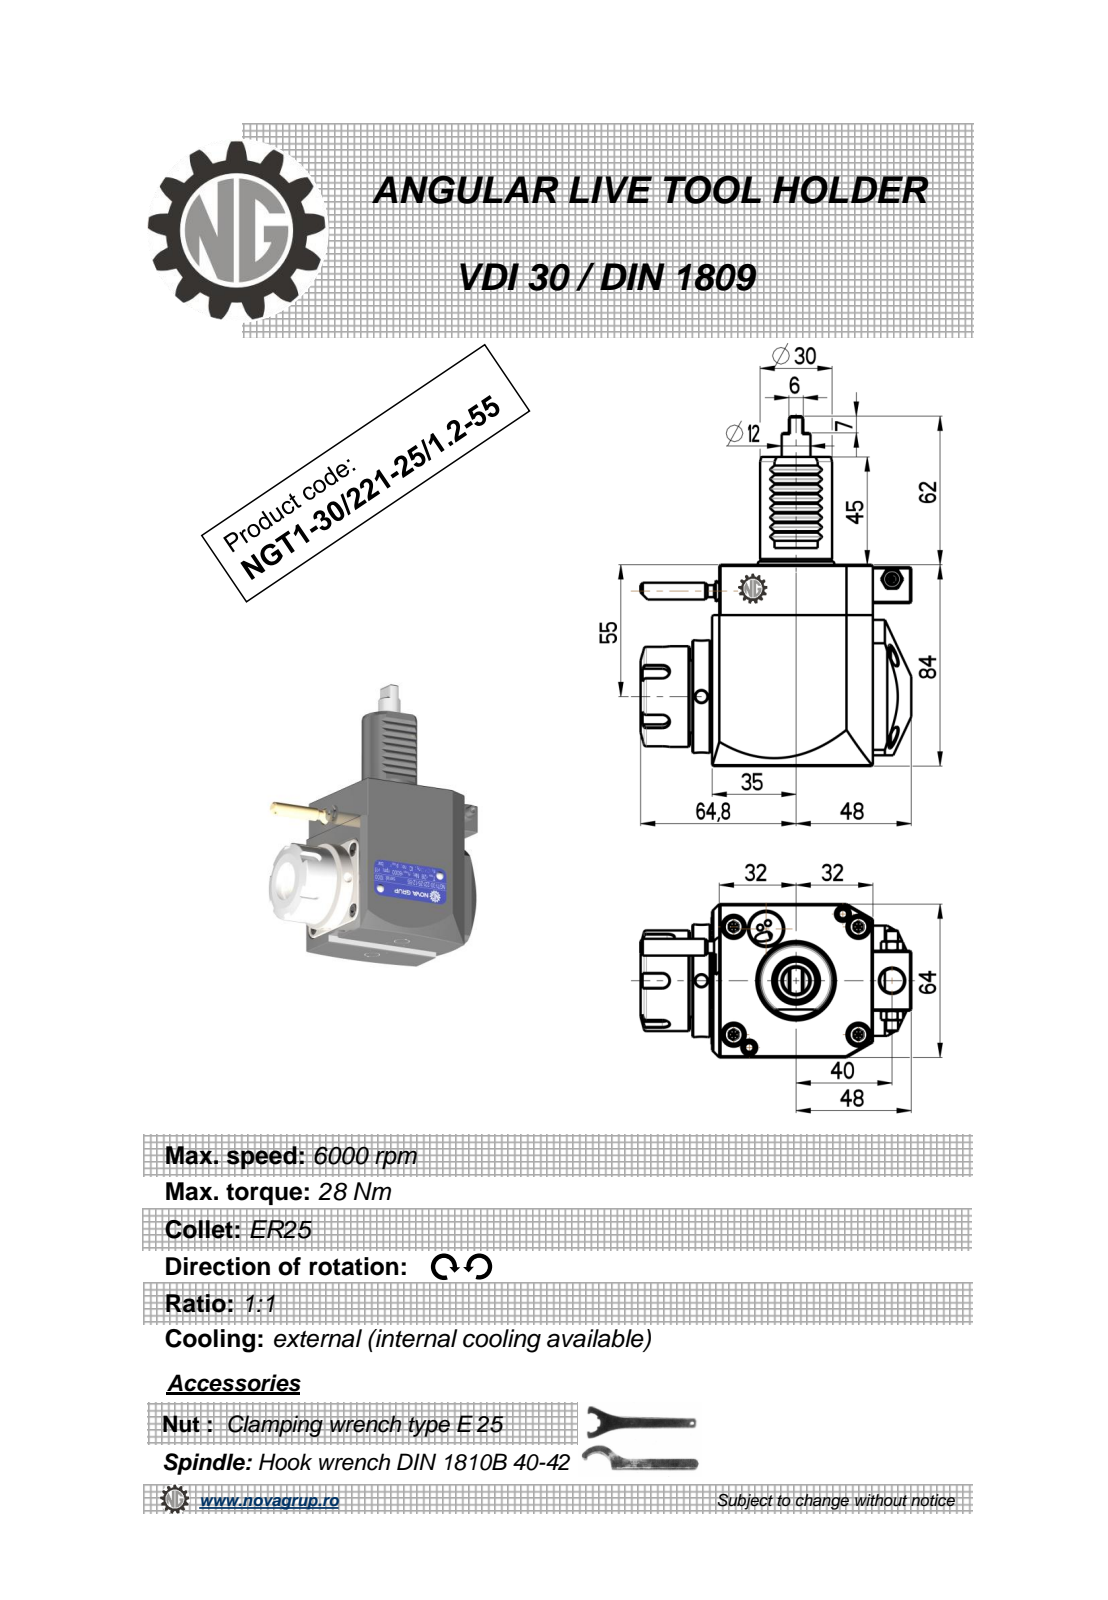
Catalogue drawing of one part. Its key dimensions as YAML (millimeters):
part_name: "NGT1_30_221_25_1_2_55"
step_written_by: "PRO/ENGINEER BY PARAMETRIC TECHNOLOGY CORPORATION, 2010280 (CONFIG_CONTROL_DESIGN)"
units: millimeters
bodies: {solids: 1, faces: 426, planar: 187, cylindrical: 88, other: 151}
overall_size: [146, 112.88, 64]
volume: 449238
surface_area: 47231
round_holes:
  - {diameter: 5, count: 2}
  - {diameter: 2.5, count: 1}
  - {diameter: 3, count: 1}
  - {diameter: 4.2, count: 1}
  - {diameter: 9.5, count: 1}
  - {diameter: 10, count: 1}
  - {diameter: 20.3, count: 1}
  - {diameter: 34, count: 1}
round_bosses_or_shafts:
  - {diameter: 8.96, count: 2}
  - {diameter: 5, count: 2}
  - {diameter: 47, count: 1}
  - {diameter: 42, count: 1}
  - {diameter: 33.4, count: 1}
  - {diameter: 33, count: 1}
  - {diameter: 30, count: 1}
  - {diameter: 12, count: 1}
partial_cylinders:
  - {radius: 0.26, count: 12}
  - {radius: 0.3, count: 8}
  - {radius: 3, count: 5}
  - {radius: 3.5, count: 4}
  - {radius: 0.8, count: 2}
  - {radius: 160, count: 2}
  - {radius: 32, count: 1}
face_to_face_distances: [64, 84, 67.2, 3, 3.2, 67, 0.5, 80, 7.5, 8]
hole_center_spacings: [14.22, 46.17, 46.5, 79.45, 93.35]
